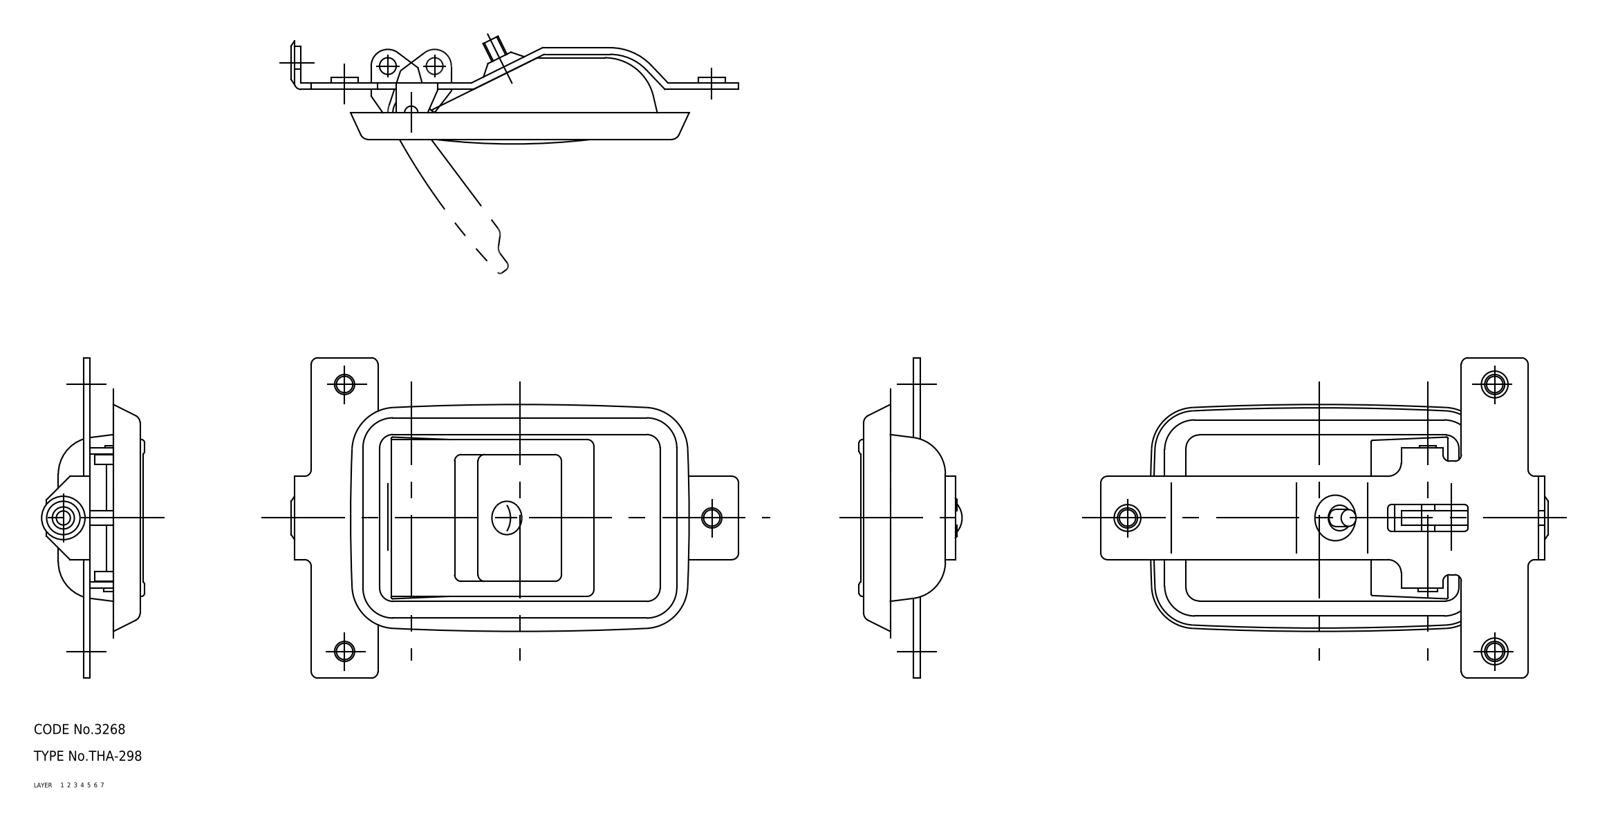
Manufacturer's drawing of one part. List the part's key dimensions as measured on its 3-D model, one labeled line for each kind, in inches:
Part name (STEP PRODUCT): washer; shaft; screw; handle (+3 more)
STEP written by: CADfix (AUTOMOTIVE_DESIGN)
Units: inches
Bodies: 6 solids, 407 faces (0 planar, 0 cylindrical, 407 other)
Overall size (bounding box): 5.274 × 3.78 × 1.271
Volume: 2.007 in³ · Surface area: 61.82 in²
